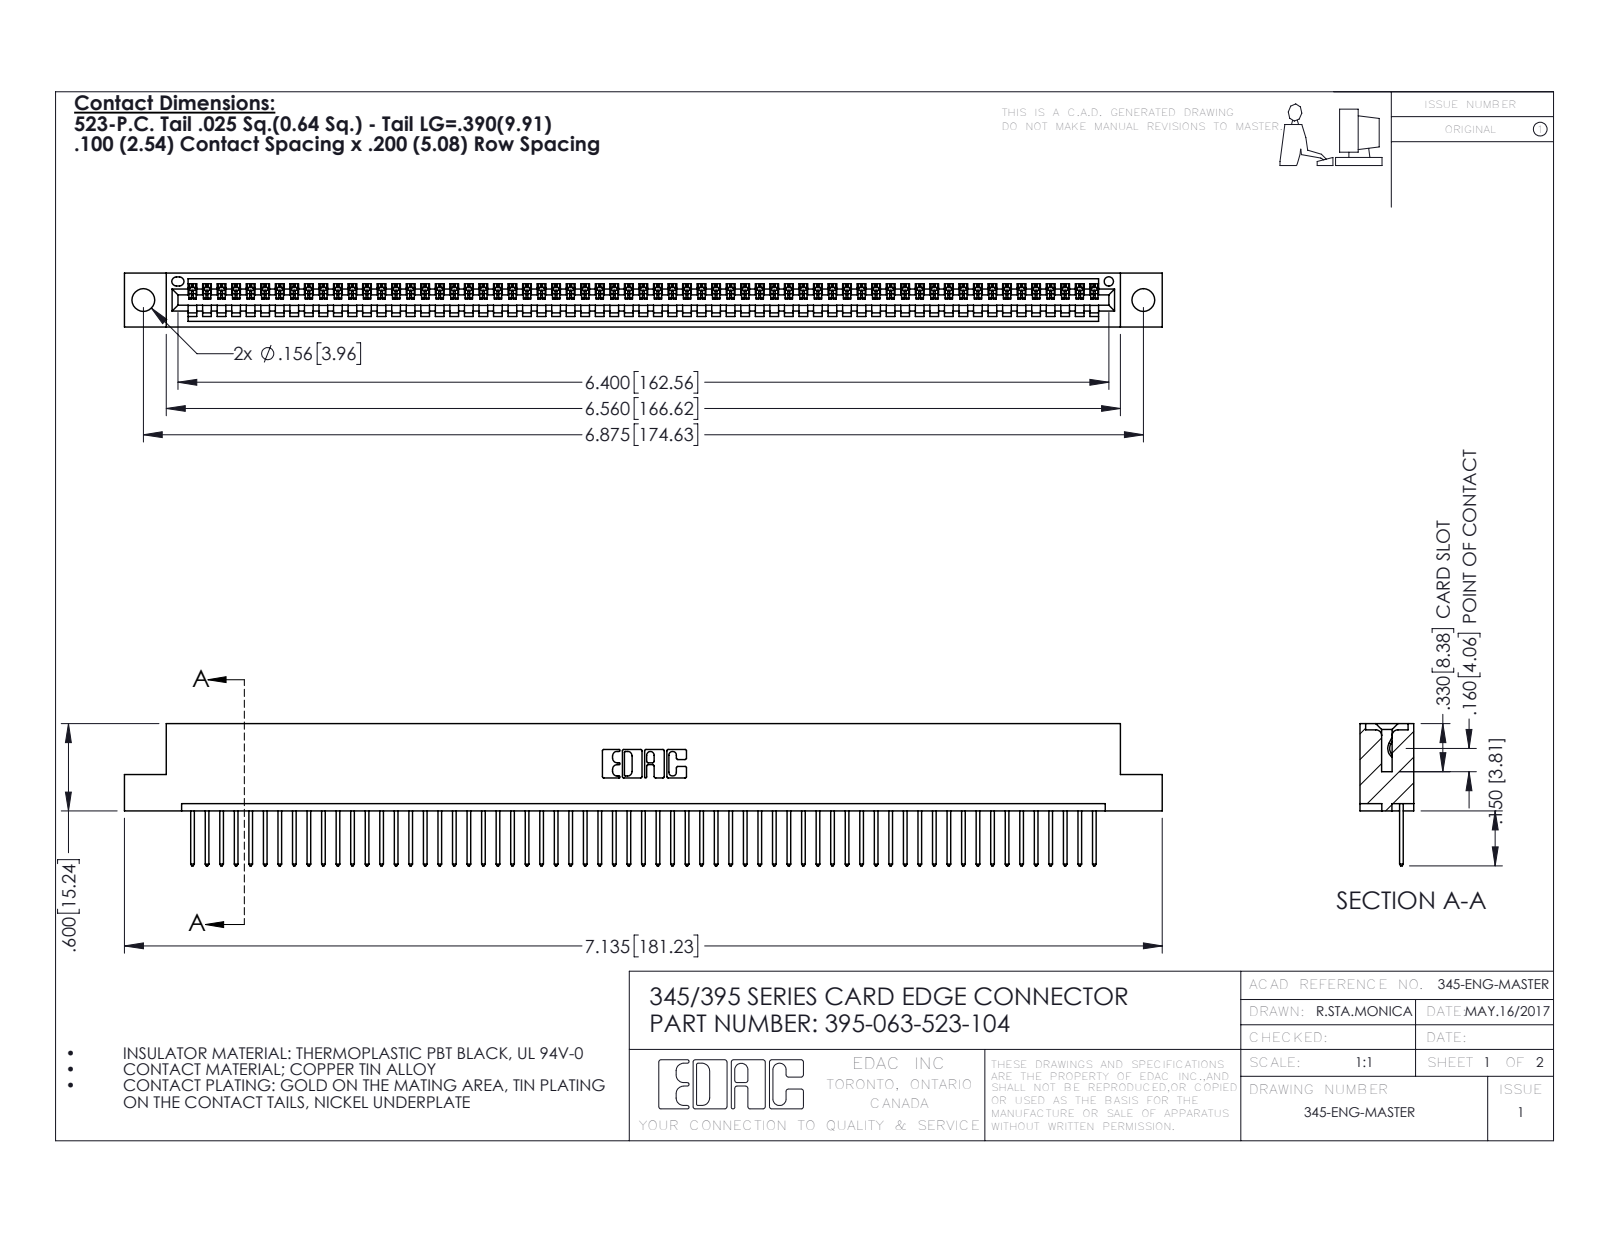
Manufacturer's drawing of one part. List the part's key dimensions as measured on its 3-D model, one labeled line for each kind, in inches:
Part name (STEP PRODUCT): 345 Part_Flush Mounting Lugs - 0.156 Dia-TH; 395-063-523-104; 345-292-001_345-293-123
STEP written by: SolidWorks 2016 (CONFIG_CONTROL_DESIGN)
Units: inches
Bodies: 64 solids, 3780 faces (2600 planar, 1180 cylindrical, 0 other)
Overall size (bounding box): 7.135 × 0.977 × 0.37
Volume: 1.054 in³ · Surface area: 35.83 in²
Round holes (diameter × count): ⌀0.156 ×2, ⌀0.064 ×1
Partial cylindrical surfaces — rounded edges, fillets, slot ends (radius × count): R0.006 ×126, R0.01 ×126, R0.01 ×22, R0.007 ×6, R0.031 ×6, R0.026 ×3, R0.031 ×2, R0.04 ×2
Main face-to-face distances: 0.298, 0.072, 0.37, 0.2, 0.098, 0.272, 0.025, 0.225, 0.149, 0.072
Hole centre spacings: 0.27, 6.639, 6.875
